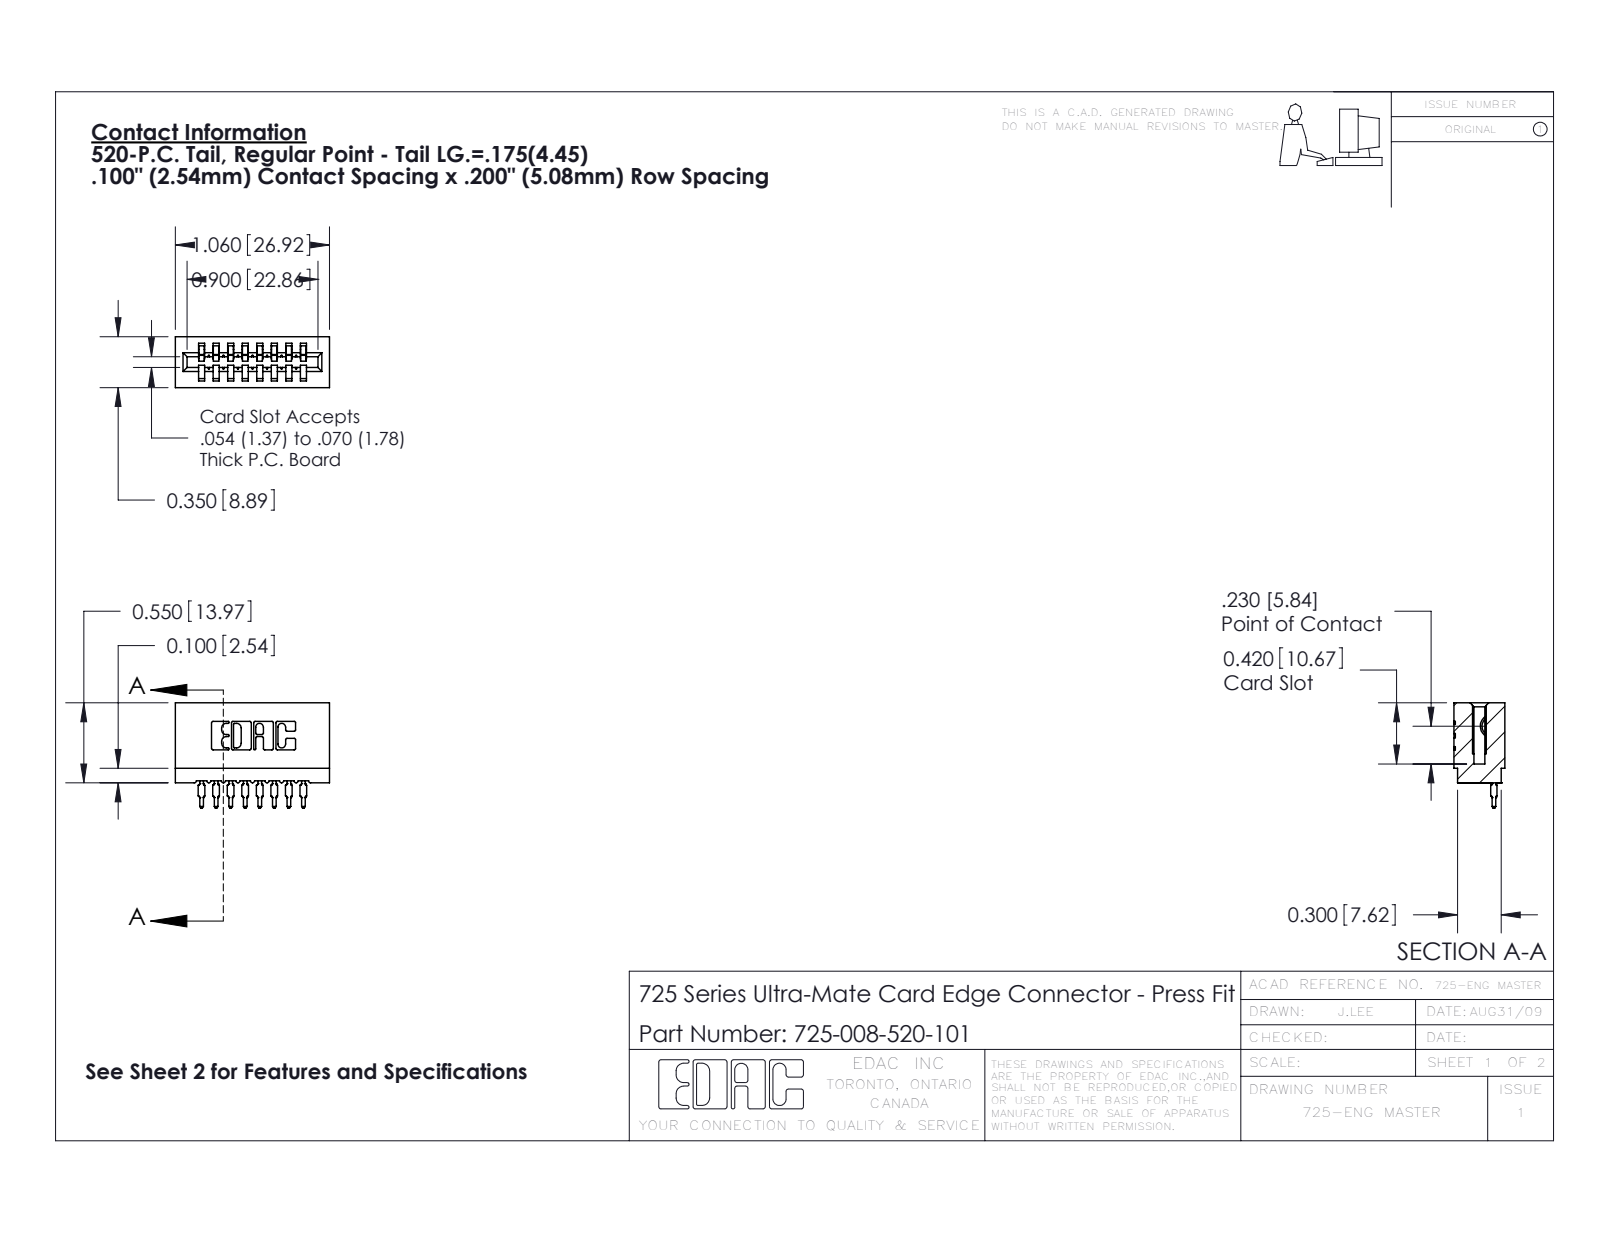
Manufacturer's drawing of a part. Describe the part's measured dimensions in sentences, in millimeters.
The part is named "725 Part_Insulator Option - 01; 745-292-001_520; 725-008-520-101". Its 3-D file was written by "SolidWorks 2016 (CONFIG_CONTROL_DESIGN)". It is 9 solids with 991 faces: 591 planar, 192 cylindrical and 208 other. Overall it measures 26.9 by 18.4 by 8.9 millimeters. Its volume is 2 210 cubic millimeters and its surface area 3 606 square millimeters. Partial cylindrical surfaces (rounded edges, fillets, slot ends): 22 of radius 0.3, 16 of radius 0.4, 16 of radius 0.5, 6 of radius 0.2, 6 of radius 0.8, 4 of radius 0.1, 4 of radius 0.3, 3 of radius 0.7. The main face-to-face distances are 2.5, 5.1, 7.6, 10.2, 1.1, 3.6, 1.5, 12.7, 6.1, 4.
